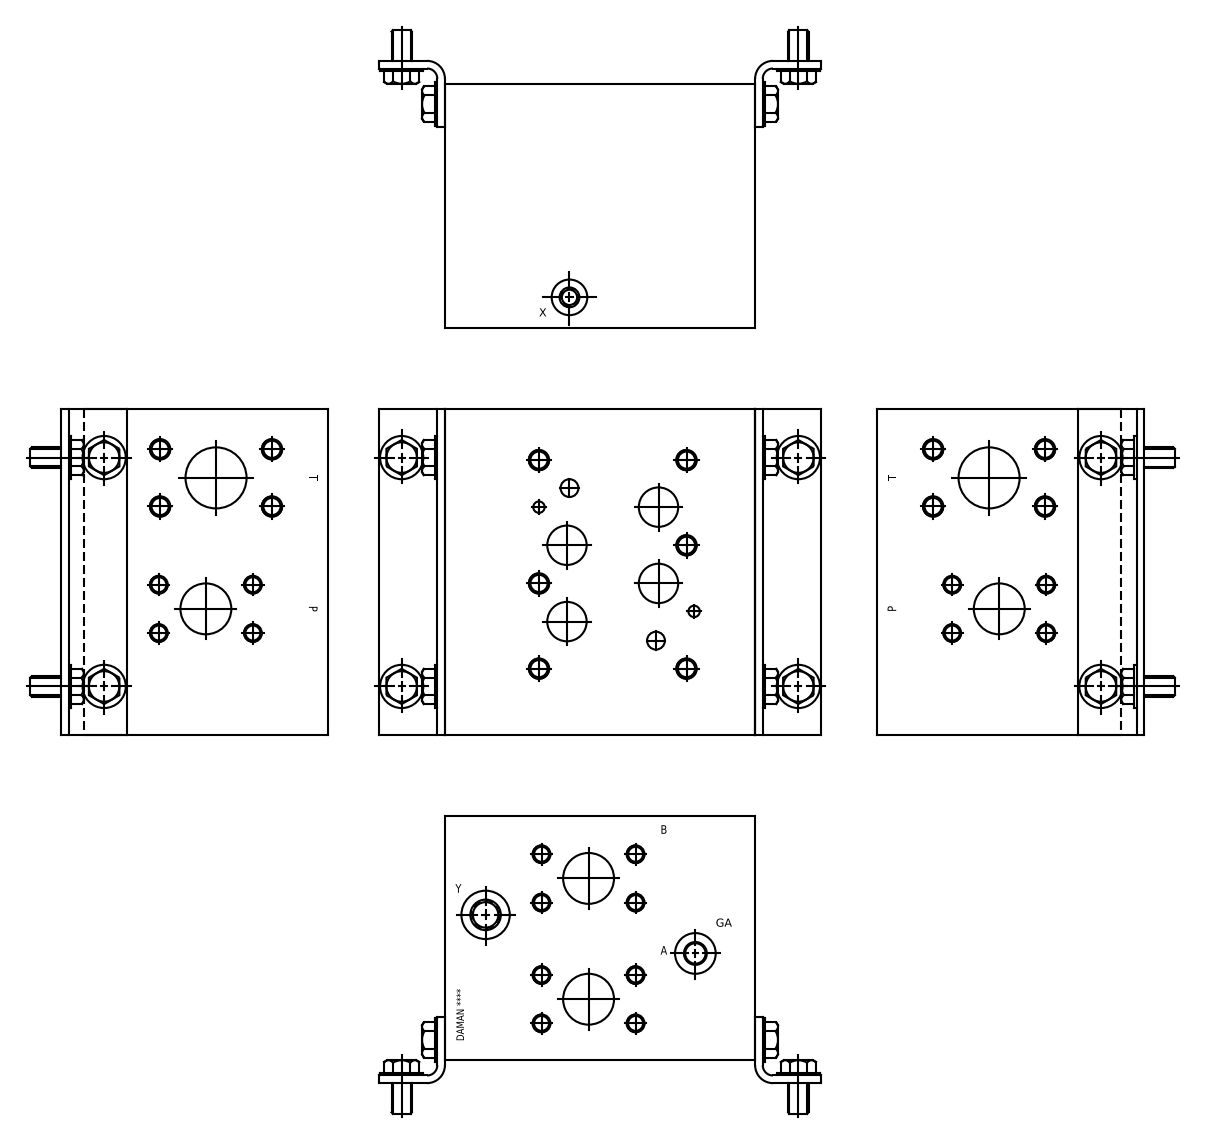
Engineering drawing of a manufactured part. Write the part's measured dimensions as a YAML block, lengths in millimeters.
part_name: "C:\\\\Program Files\\\\PARO\\\\Hydroman 800\\\\Export\\\\AD08HP015F_1_3D"
step_written_by: "Autodesk Inventor 2011 (AUTOMOTIVE_DESIGN)"
units: millimeters
bodies: {solids: 1, faces: 126, planar: 12, cylindrical: 60, other: 54}
overall_size: [203.2, 193.68, 152.4]
volume: 5803000
surface_area: 248529
round_holes:
  - {diameter: 9.35, count: 15}
  - {diameter: 10.72, count: 12}
  - {diameter: 24.61, count: 4}
  - {diameter: 31.75, count: 3}
  - {diameter: 7.14, count: 2}
  - {diameter: 11.13, count: 2}
  - {diameter: 9.53, count: 1}
  - {diameter: 9.88, count: 1}
  - {diameter: 12.29, count: 1}
  - {diameter: 12.4, count: 1}
  - {diameter: 12.7, count: 1}
  - {diameter: 12.9, count: 1}
face_to_face_distances: [152.4, 193.68, 203.2, 0.79, 202.41, 201.62, 3.28, 2.49, 199.13, 199.92]
hole_center_spacings: [33.01, 58.72, 66.02, 30.17, 30.18, 95.14, 39.23, 58.73]
